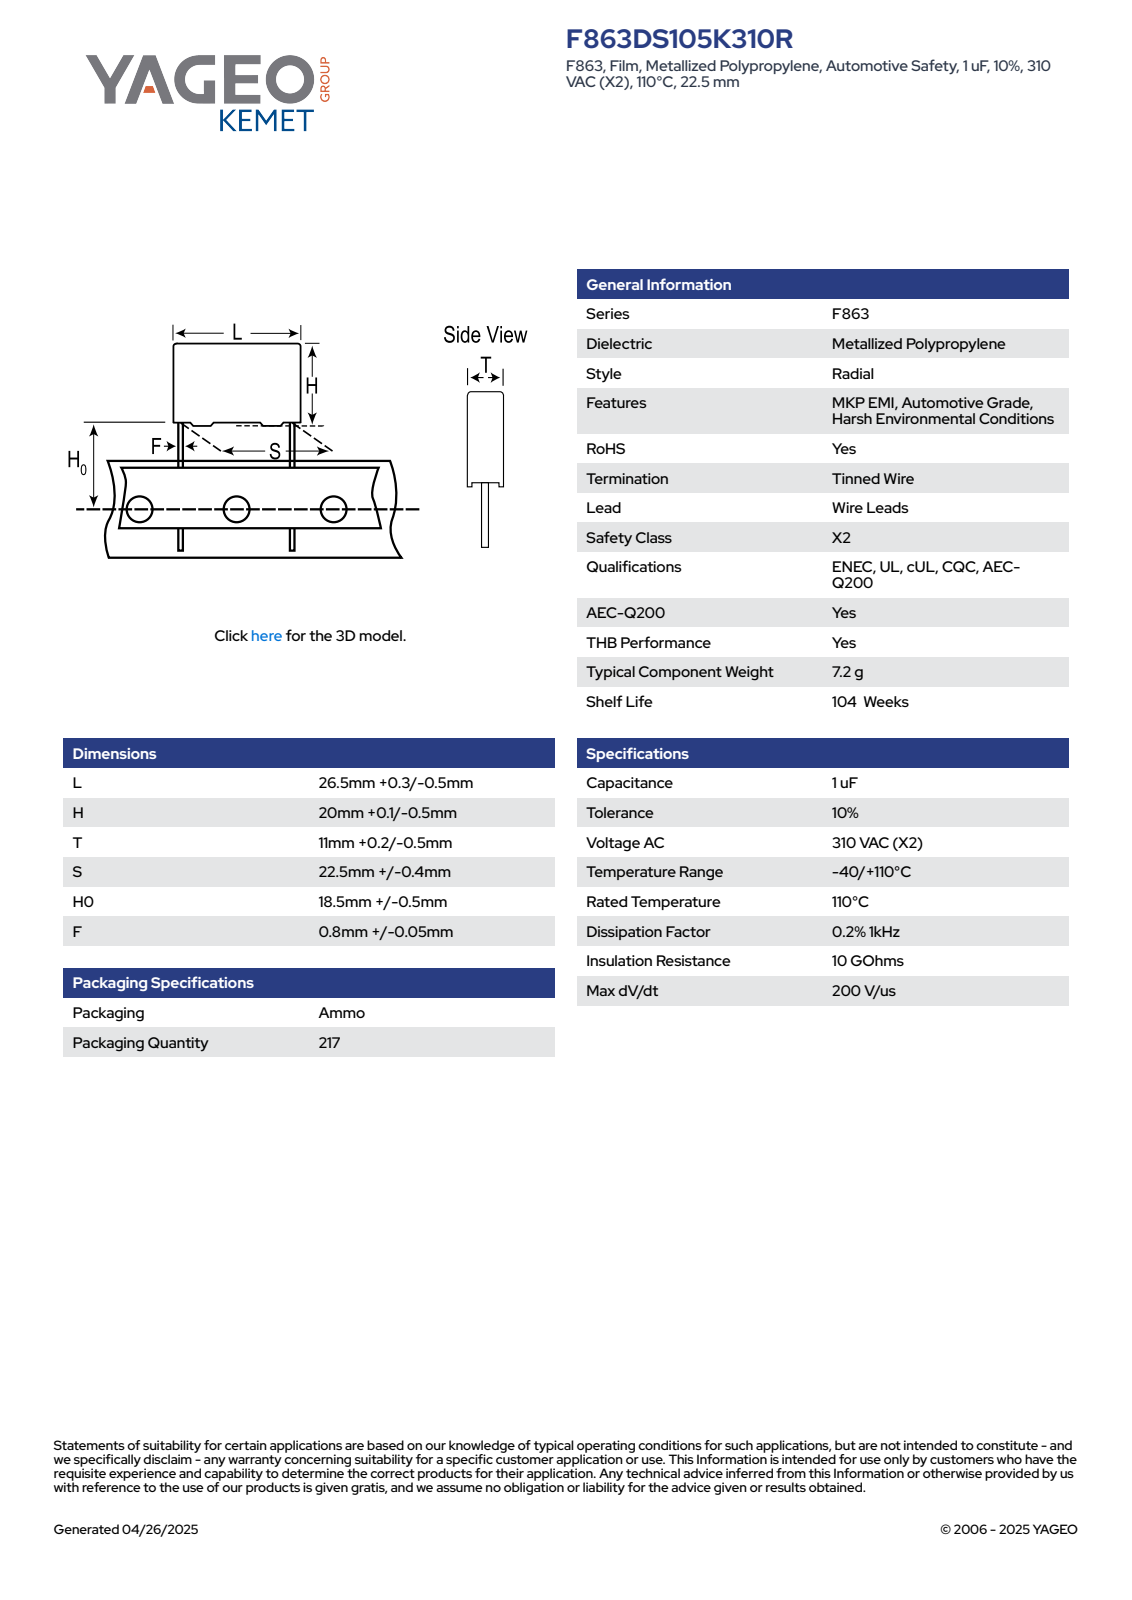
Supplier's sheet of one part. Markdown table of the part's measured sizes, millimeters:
| quantity | value |
| --- | --- |
| part name | CFR_RB2_26.5X20X11_L26.8H20.1T11.2S22.5H019F0.85 |
| STEP written by | SolidWorks 2020 (AUTOMOTIVE_DESIGN) |
| units | millimeters |
| bodies | 4 solids, 85 faces (77 planar, 8 cylindrical, 0 other) |
| overall size | 39.1 × 26.8 × 11.21 |
| volume | 5 852 mm³ |
| surface area | 2 271 mm² |
| round bosses / shafts (diameter × count) | 0.85 × 2 |
| partial cylindrical surfaces (radius × count) | 0.5 × 4 |
| main face-to-face distances | 11.2, 19.35, 26.8, 19.41, 0.75, 0.69, 20.1, 0.89, 25.91, 11.21 |
